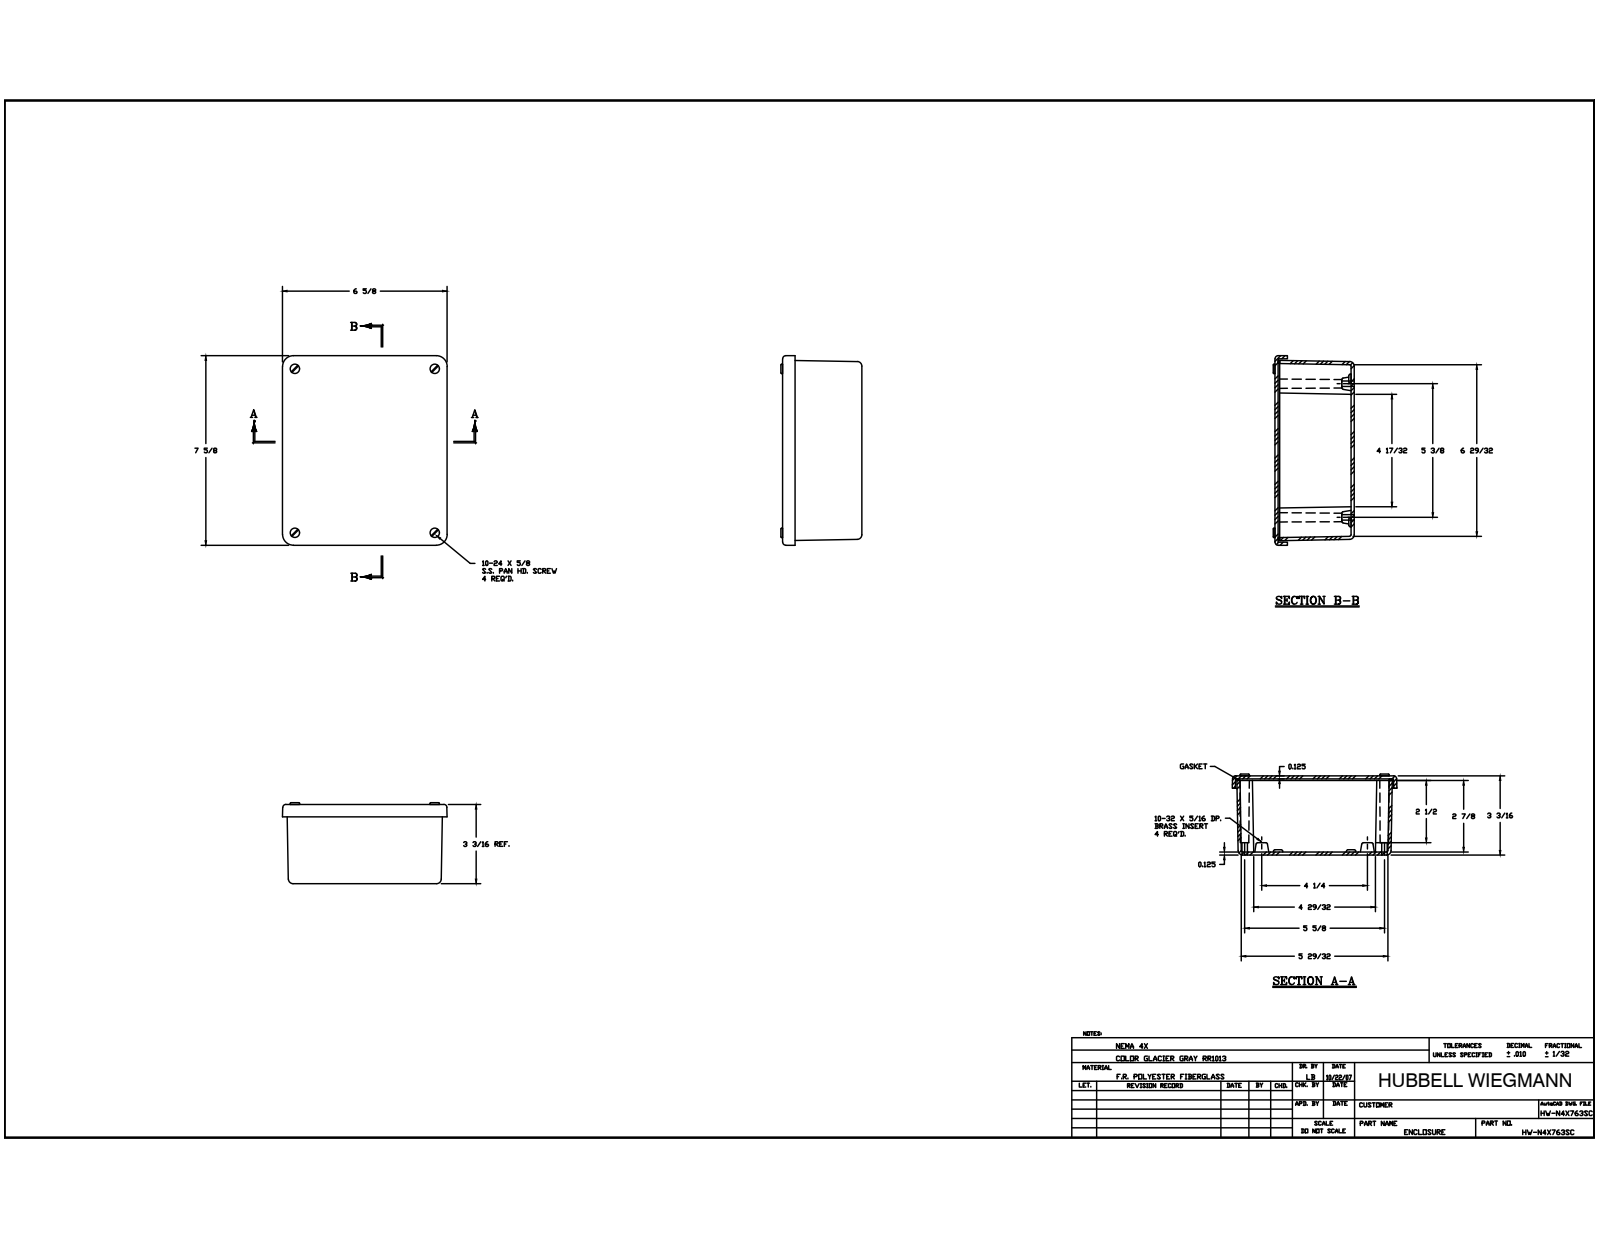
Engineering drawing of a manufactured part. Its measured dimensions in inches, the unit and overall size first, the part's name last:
Units: inches
Overall size (bounding box): 7.66 × 6.633 × 3.306
Round holes (diameter × count): ⌀0.219 ×8, ⌀0.145 ×4, ⌀0.156 ×4, ⌀0.21 ×4, ⌀0.25 ×4, ⌀0.281 ×4
Round bosses / shafts (diameter × count): ⌀0.375 ×4, ⌀0.371 ×4, ⌀0.218 ×4, ⌀0.177 ×4, ⌀0.281 ×2
Partial cylindrical surfaces — rounded edges, fillets, slot ends (radius × count): R0.031 ×20, R0.012 ×16, R0.044 ×8, R0.125 ×4, R0.187 ×4
Main face-to-face distances: 0.125, 3.063, 3.188, 2.938, 0.5, 0.625, 0.125, 0.188, 0.063, 3
Hole centre spacings: 5.375, 5.419, 5.617, 6.024, 6.635, 7.758, 0.609, 0.687
Volume: 28.09 in³ · Surface area: 392.2 in²
Bodies: 15 solids, 356 faces (148 planar, 112 cylindrical, 96 other)
Part name (STEP PRODUCT): WPF763 BOX; 10-32 X0.3125 DP BRASS INSERT; 10-24X0.50 DP BRASS INSERT; WPF763 CVR (+4 more)
STEP written by: Autodesk Inventor 2014 (AUTOMOTIVE_DESIGN)
